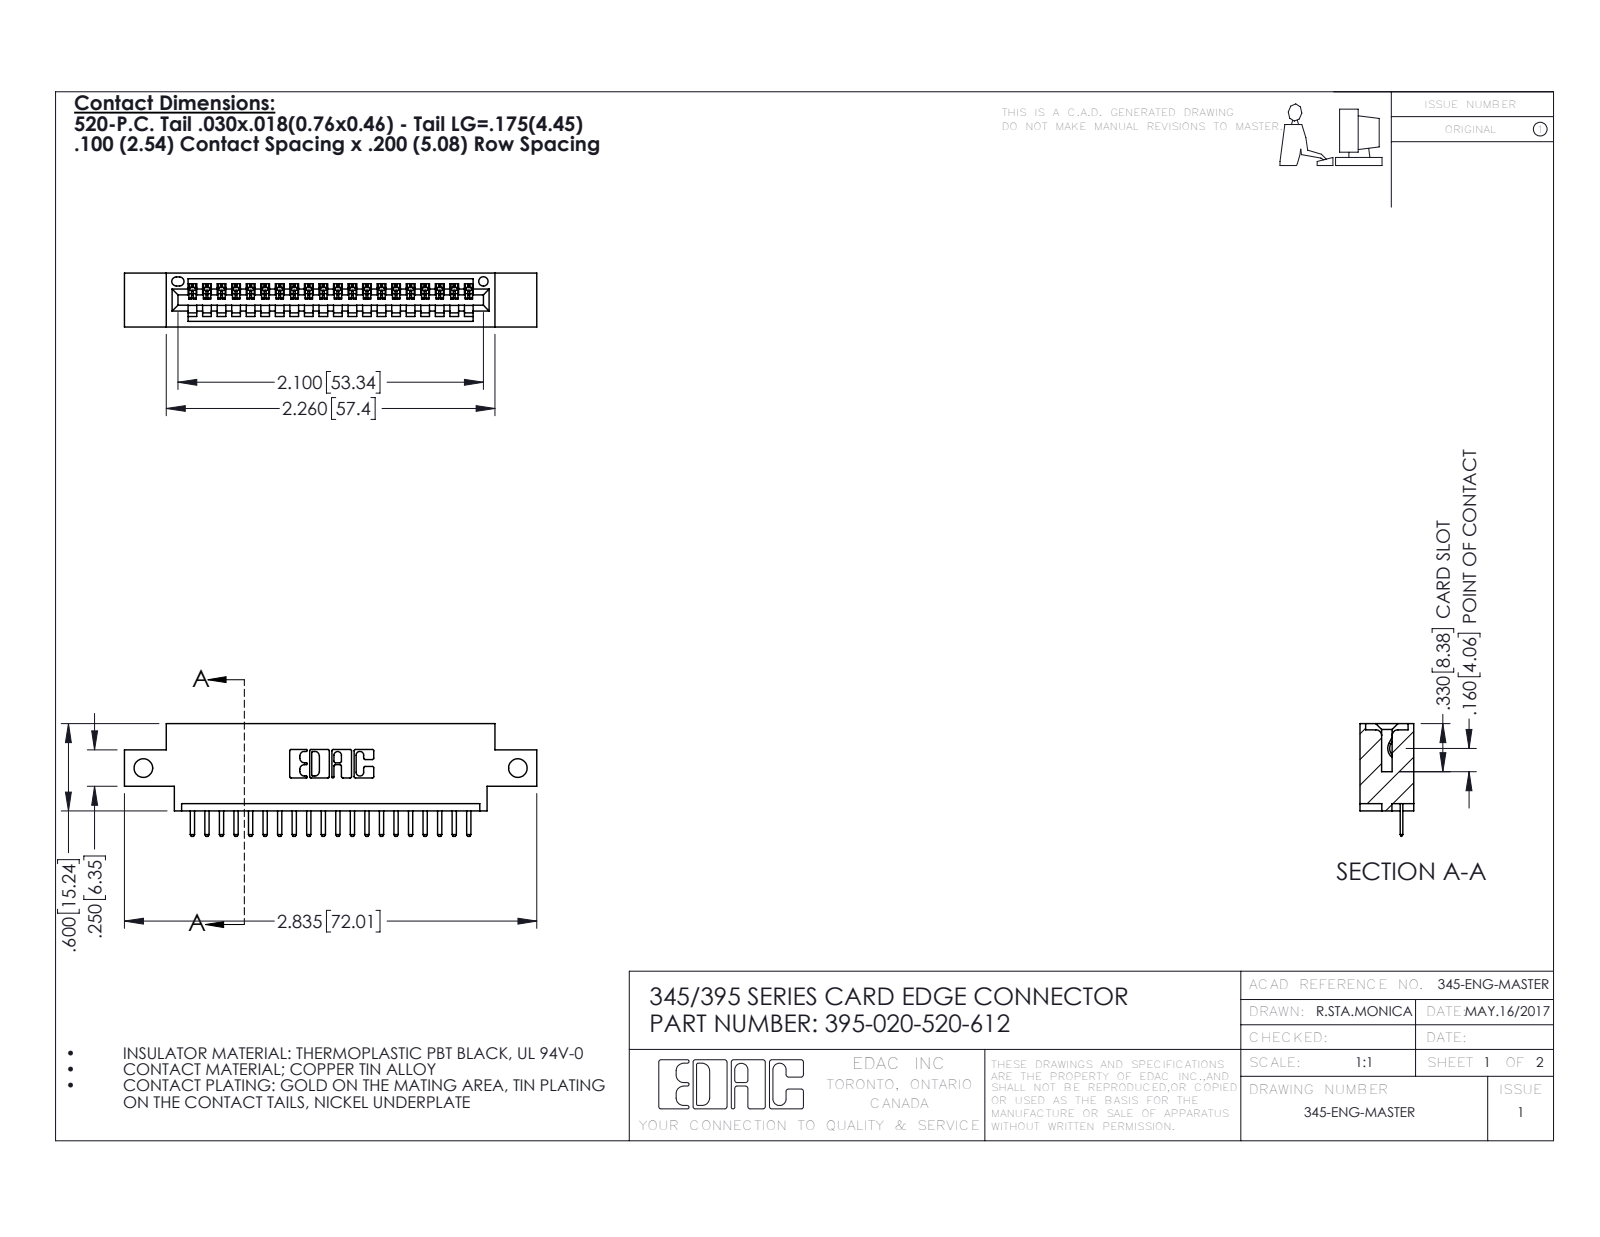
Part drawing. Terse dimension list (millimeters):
name: 395-020-520-612; 345 Part_0.170 Offset - Side Mount; 345-292-001_345-293-120
written by: SolidWorks 2016 (CONFIG_CONTROL_DESIGN)
unit: mm
bodies: 21 solids, 1370 faces (924 planar, 446 cylindrical, 0 other)
size: 72 × 19.7 × 9.4
volume: 6 410 mm³; area: 8 006 mm²
holes: 2× ⌀3.3, 1× ⌀1.6
rounds: 42× R0.3, 40× R0.2, 22× R0.3, 6× R0.2, 6× R0.8, 3× R0.7, 2× R0.8, 2× R1
face distances: 9.4, 1.8, 7.6, 5.1, 2.5, 6.9, 0.6, 5.7, 1.8, 4.4
hole spacings: 65.4
